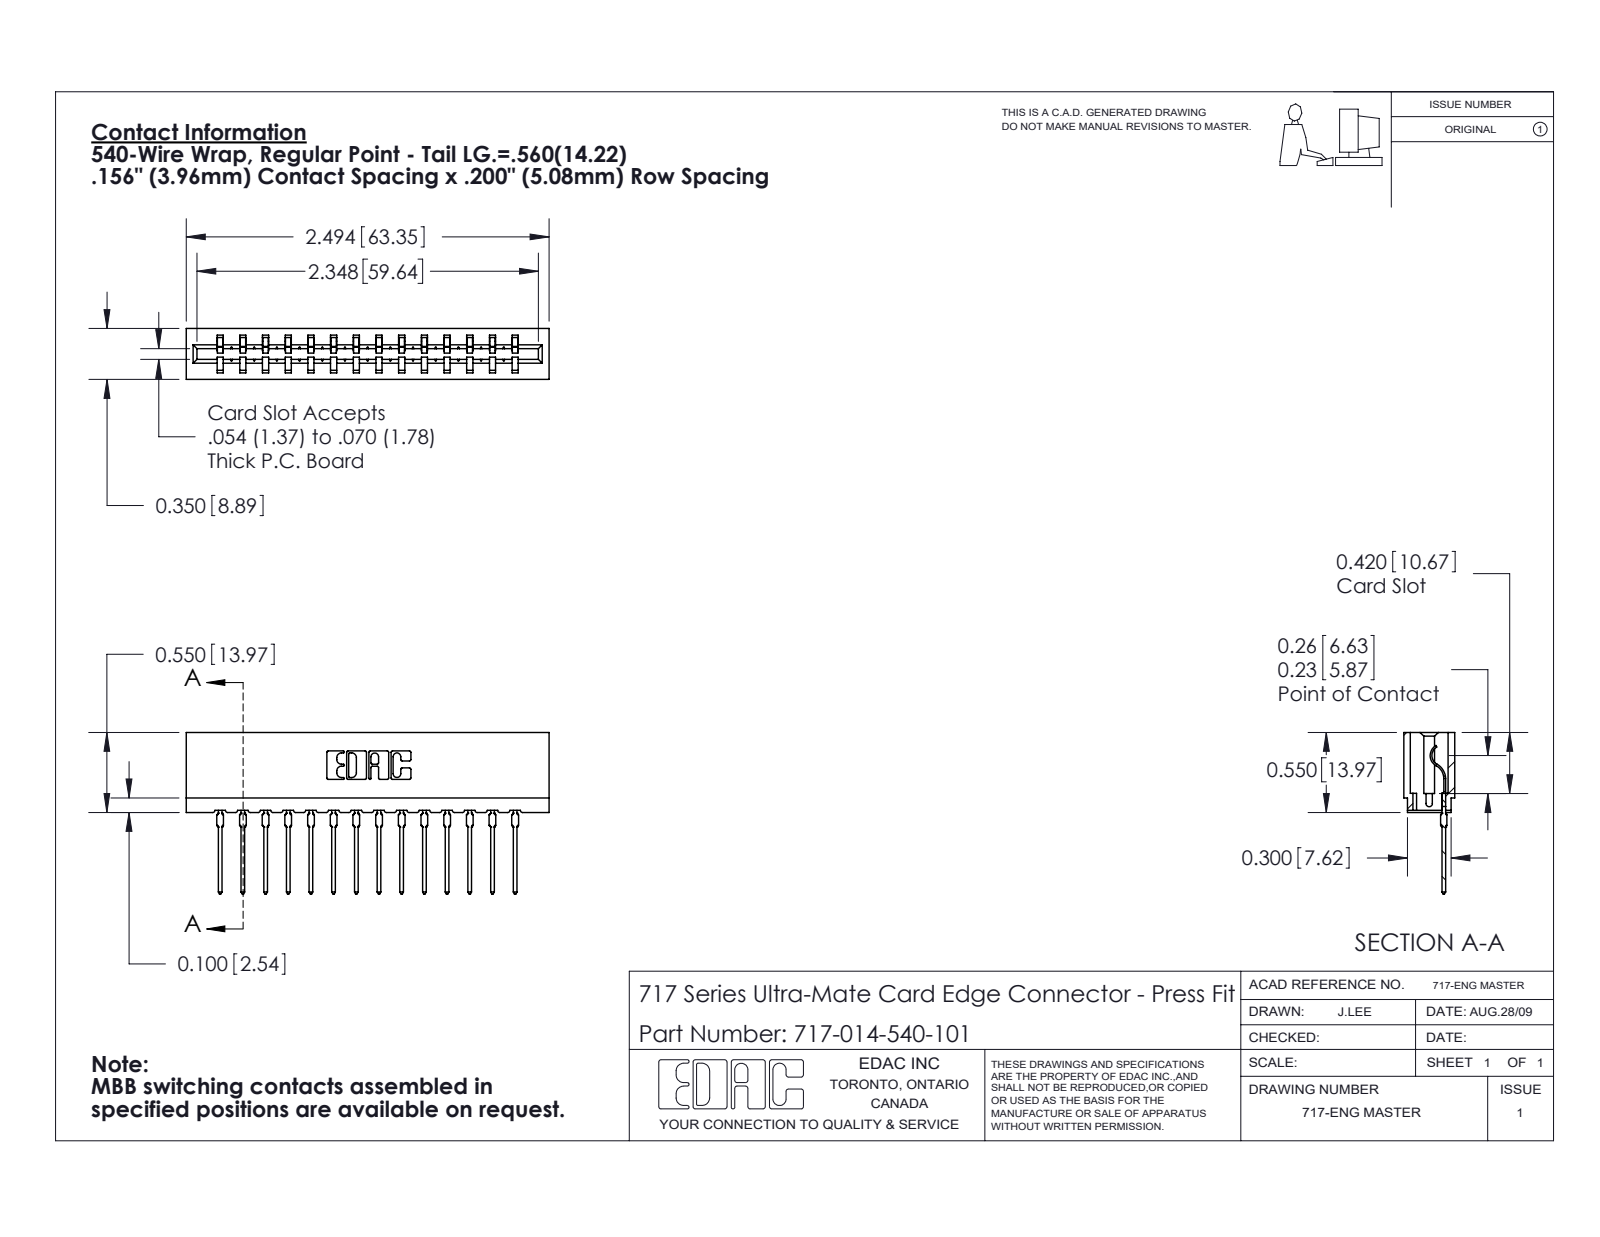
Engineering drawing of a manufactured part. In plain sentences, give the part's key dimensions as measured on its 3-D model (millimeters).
The part is named "717-014-540-101; 745-292-001_540; 717 Part_Insulator Option - 06". Its 3-D file was written by "SolidWorks 2020 (CONFIG_CONTROL_DESIGN)". It is 15 solids with 1676 faces: 1006 planar, 306 cylindrical and 364 other. Overall it measures 63.3 by 28.2 by 8.9 millimeters. Its volume is 5 510 cubic millimeters and its surface area 7 594 square millimeters. Partial cylindrical surfaces (rounded edges, fillets, slot ends): 28 of radius 0.4, 28 of radius 0.5, 22 of radius 0.3, 6 of radius 0.2, 6 of radius 0.8, 4 of radius 0.1, 4 of radius 0.3, 3 of radius 0.7. The main face-to-face distances are 5.4, 3.5, 4, 8.9, 15.8, 11.9, 5, 7.9, 1.9, 9.
